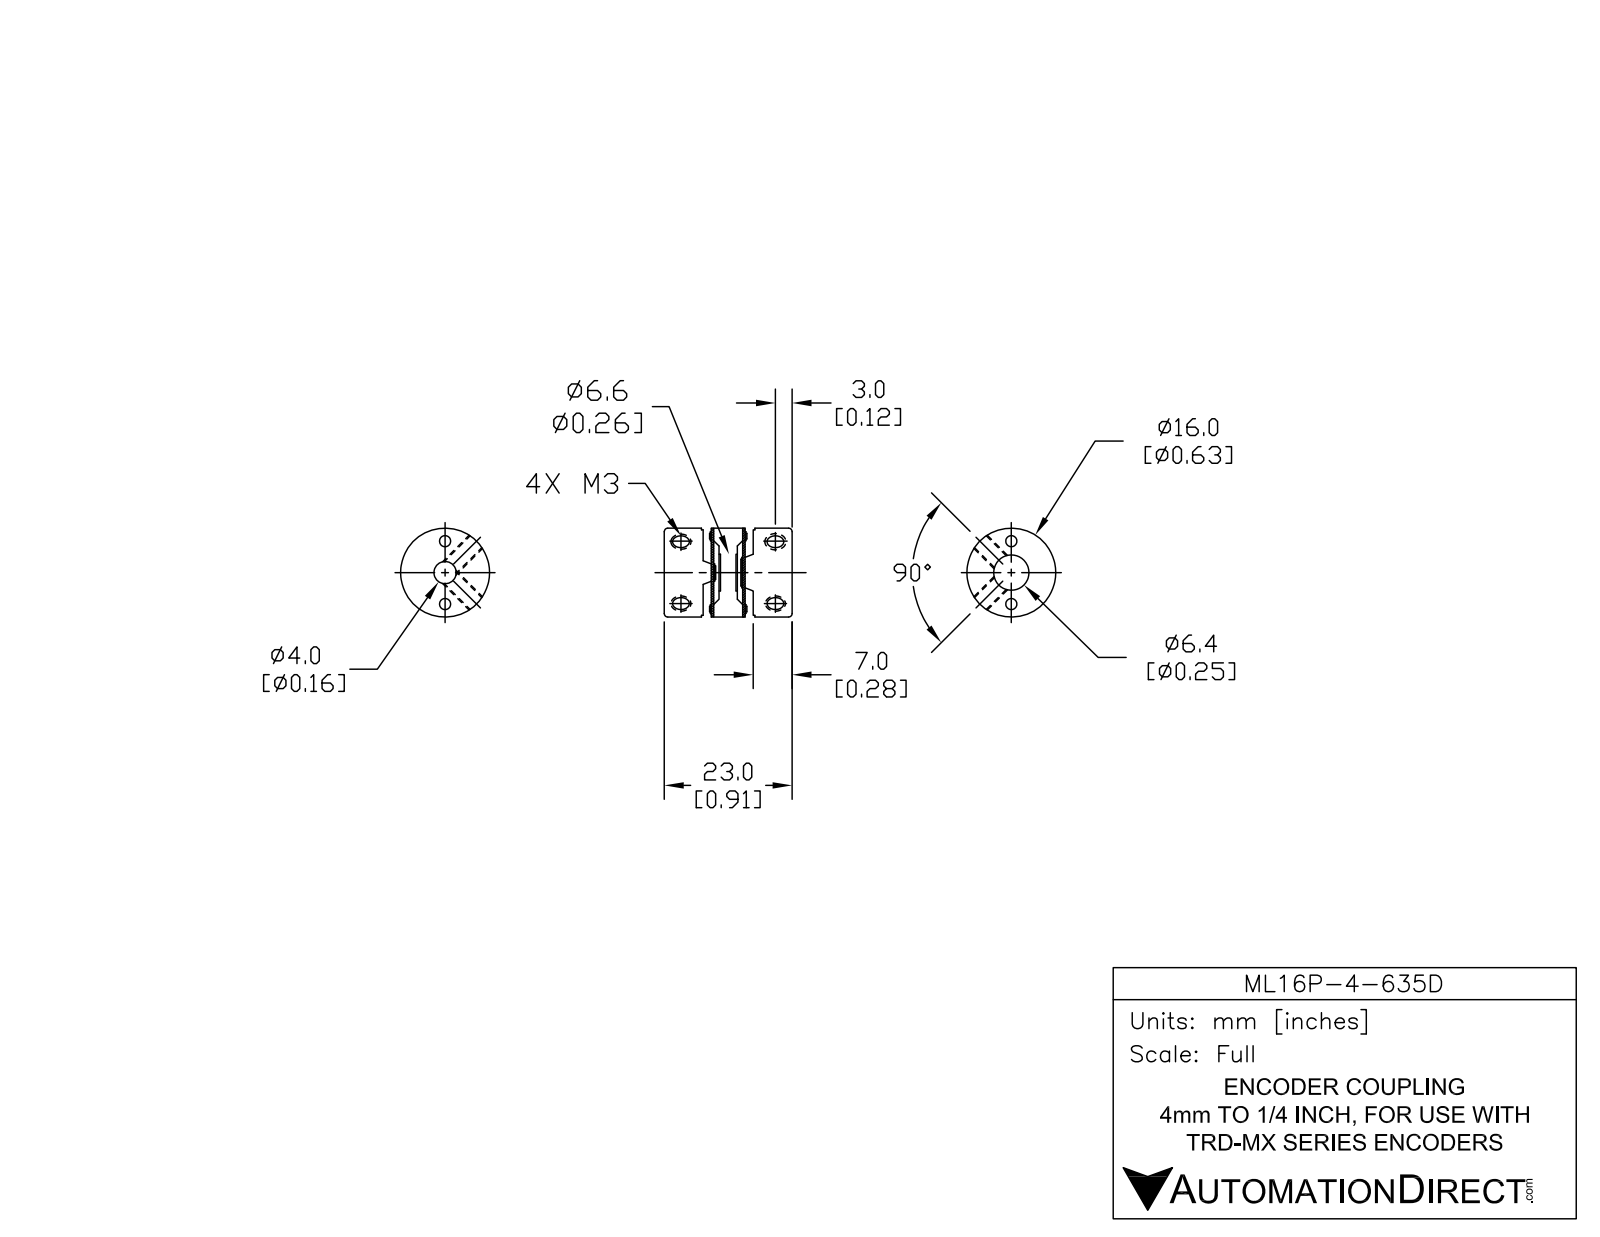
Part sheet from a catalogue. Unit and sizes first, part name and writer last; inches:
Units: inches
Overall size (bounding box): 0.906 × 0.63 × 0.63
Round holes (diameter × count): ⌀0.118 ×4, ⌀0.094 ×2, ⌀0.157 ×1, ⌀0.25 ×1, ⌀0.26 ×1, ⌀0.299 ×1
Round bosses / shafts (diameter × count): ⌀0.63 ×1
Main face-to-face distances: 0.059, 0.315, 0.039, 0.256, 0.276, 0.335, 0.591, 0.63, 0.571, 0.02
Hole centre spacings: 0.232, 0.669, 0.465
Volume: 0.197 in³ · Surface area: 4.937 in²
Bodies: 1 solid, 158 faces (86 planar, 36 cylindrical, 36 other)
Part name (STEP PRODUCT): ML16P-4-635
STEP written by: SolidWorks 2016 (AUTOMOTIVE_DESIGN)
